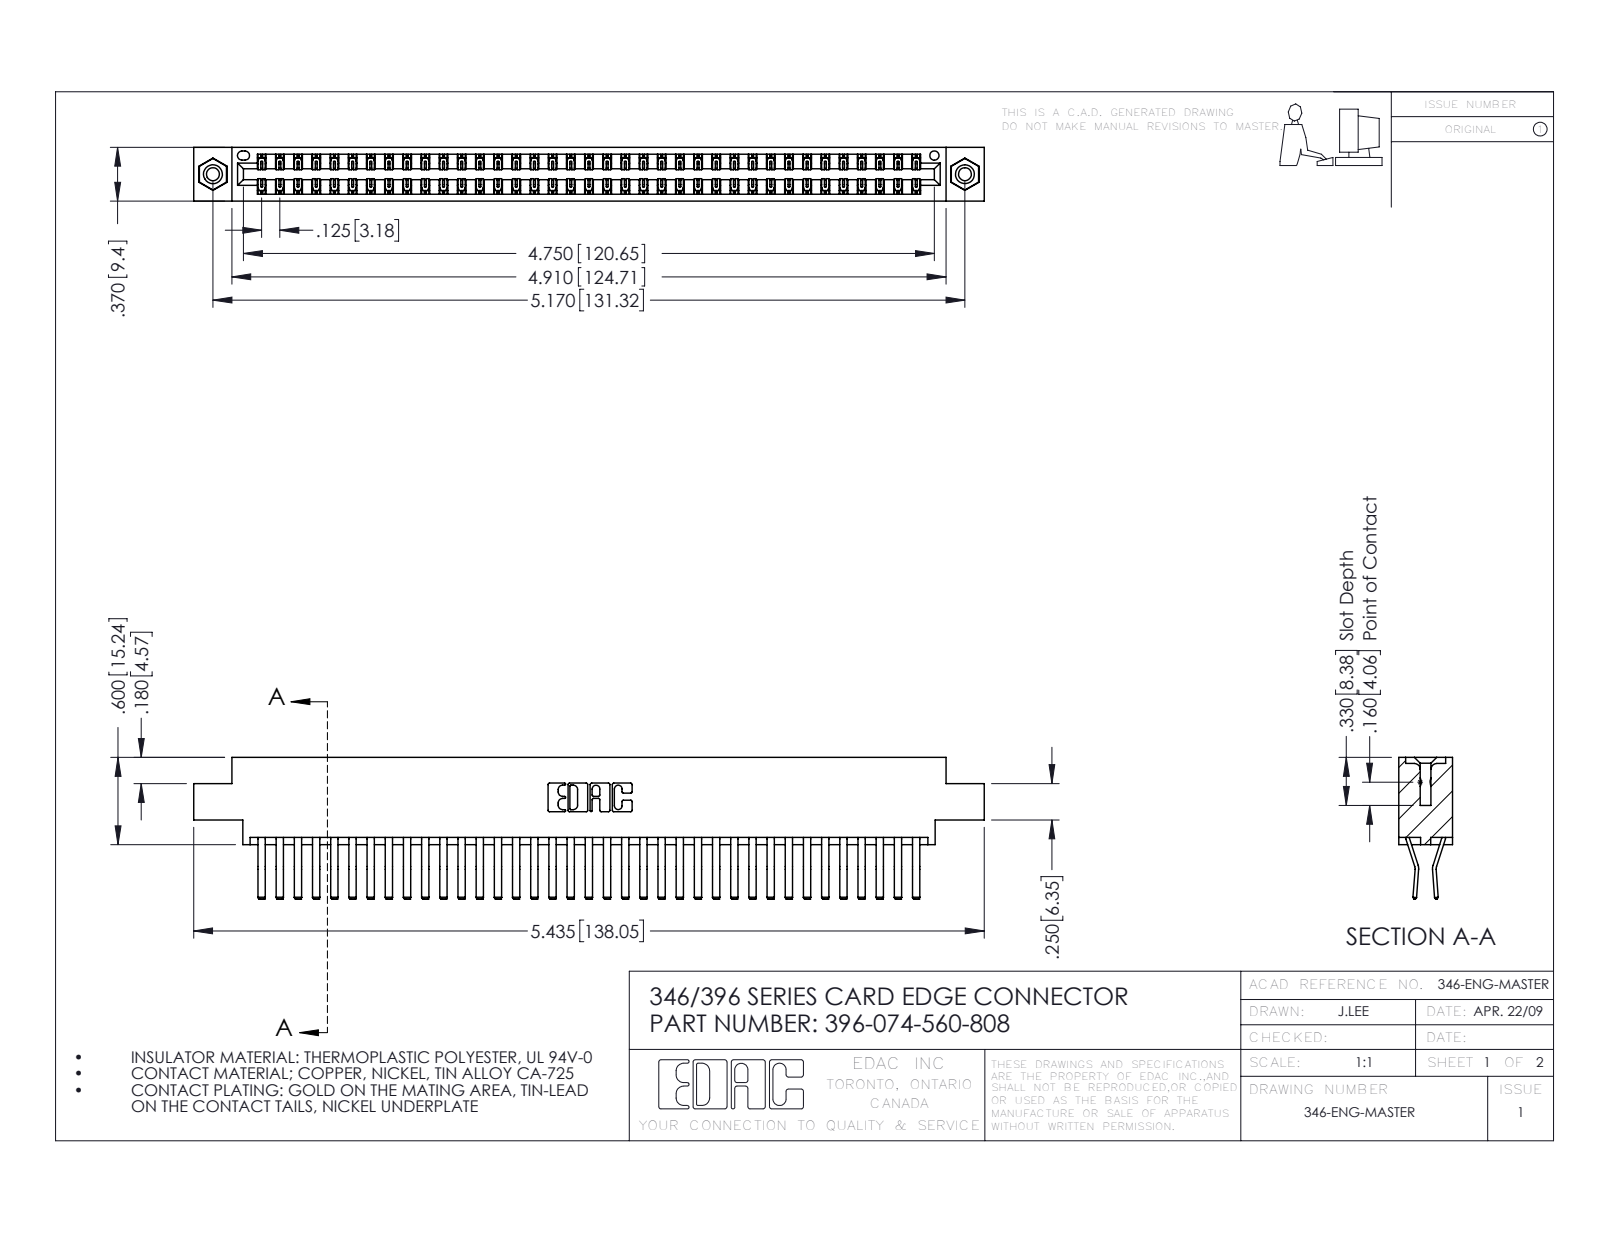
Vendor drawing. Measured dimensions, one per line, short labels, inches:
name: 345-250-001_345-250-003-102; 346 Part_0.170 Offset - 0.156 Dia-TI; 345-292-001_560 Tail; 396-074-560-808
written by: SolidWorks 2016 (CONFIG_CONTROL_DESIGN)
unit: in
bodies: 77 solids, 4182 faces (2702 planar, 1464 cylindrical, 16 other)
size: 5.435 × 0.975 × 0.37
volume: 0.839 in³; area: 31.48 in²
holes: 2× ⌀0.089, 2× ⌀0.125, 2× ⌀0.156, 1× ⌀0.064
bosses: 2× ⌀0.155
rounds: 111× R0.006, 22× R0.01, 6× R0.007, 6× R0.031, 3× R0.026, 2× R0.01, 2× R0.014, 2× R0.022
face distances: 0.048, 0.322, 0.37, 0.025, 0.25, 0.072, 0.298, 0.275, 0.222, 0.148
hole spacings: 0.246, 4.961, 5.17
